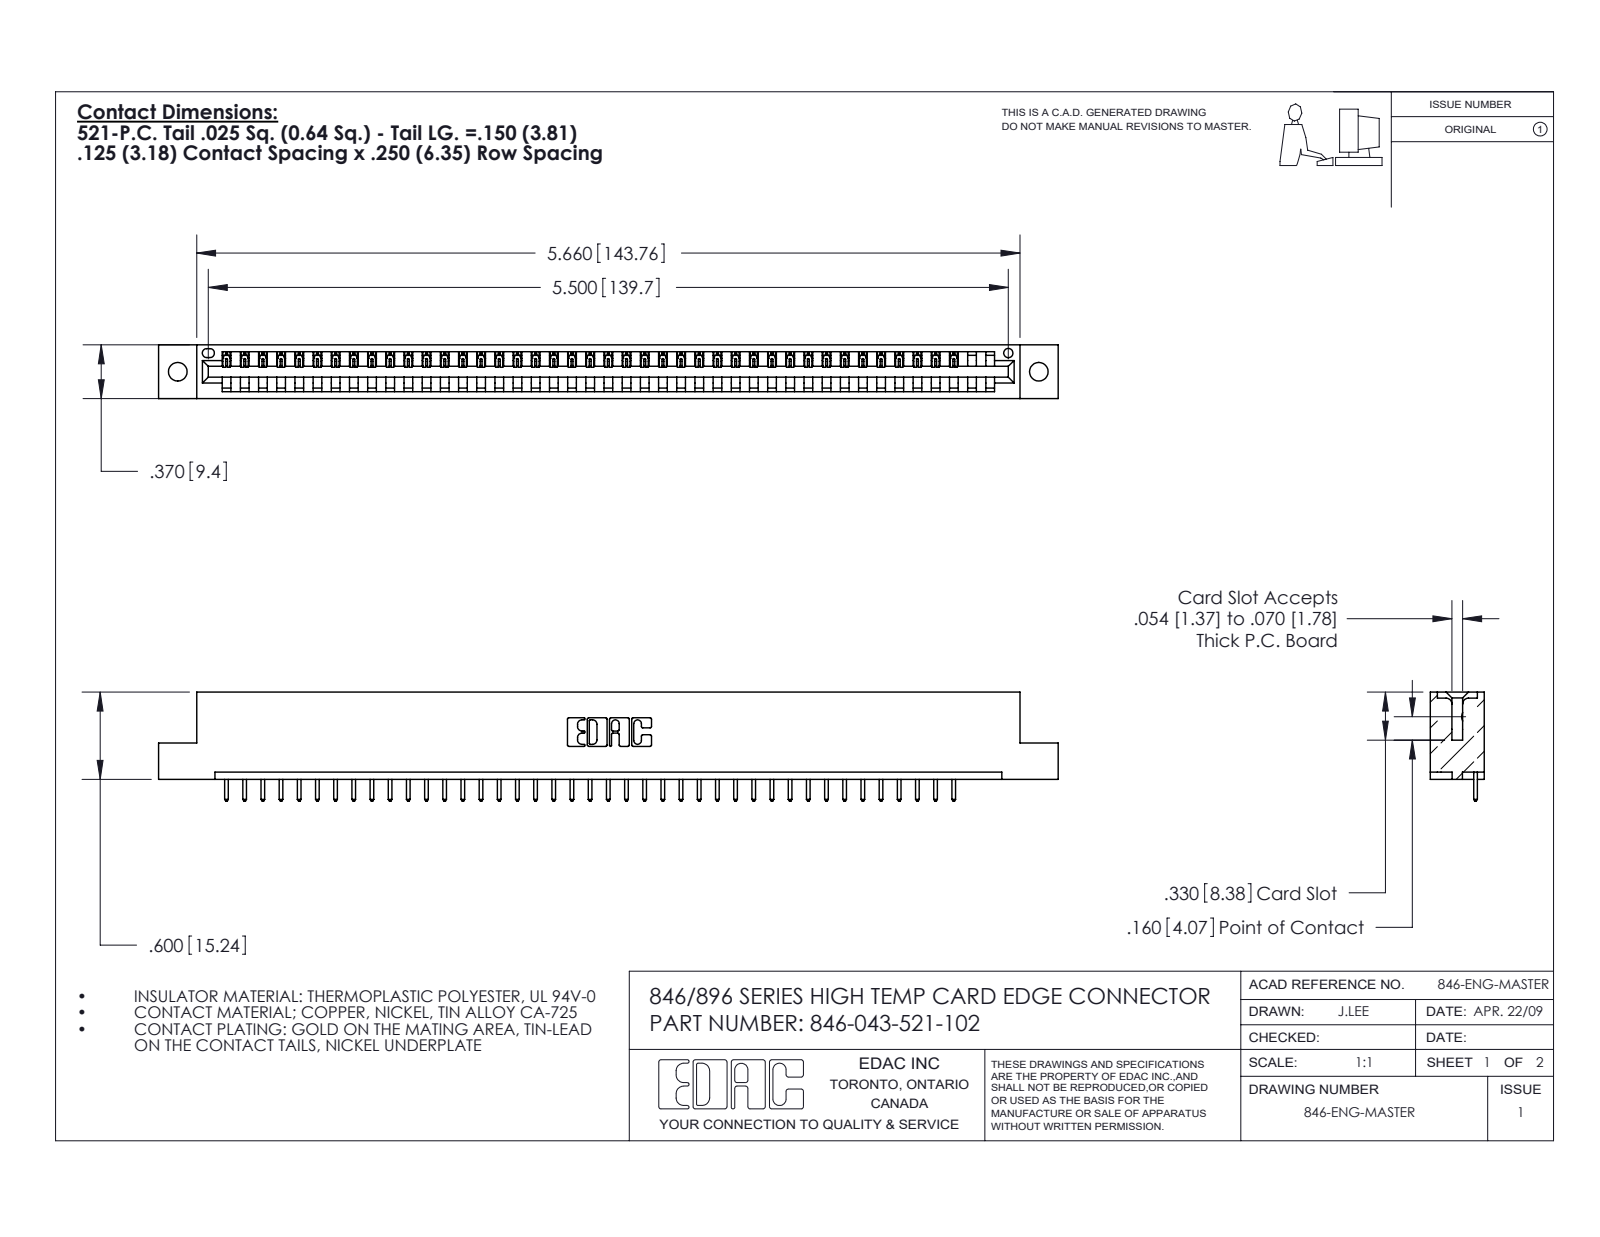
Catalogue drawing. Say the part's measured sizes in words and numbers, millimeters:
The part is named "346 Part_Flush Mounting Lugs - 0.128 Dia; 345-292-001_345-293-121; 346-043-521-102". Its 3-D file was written by "SolidWorks 2016 (CONFIG_CONTROL_DESIGN)". It is 44 solids with 2616 faces: 1796 planar, 820 cylindrical and 0 other. Overall it measures 157.1 by 19.1 by 9.4 millimeters. Its volume is 14 900 cubic millimeters and its surface area 17 860 square millimeters. Round holes: 2 of diameter 3.3, 1 of diameter 1.6. Partial cylindrical surfaces (rounded edges, fillets, slot ends): 86 of radius 0.2, 86 of radius 0.3, 22 of radius 0.3, 6 of radius 0.2, 6 of radius 0.8, 3 of radius 0.7, 2 of radius 0.8, 2 of radius 1. The main face-to-face distances are 1.2, 8.2, 9.4, 6.4, 1.8, 7.6, 0.6, 3.8, 5.6, 2.5. The hole center spacings are 6.2, 145.1, 150.4.
